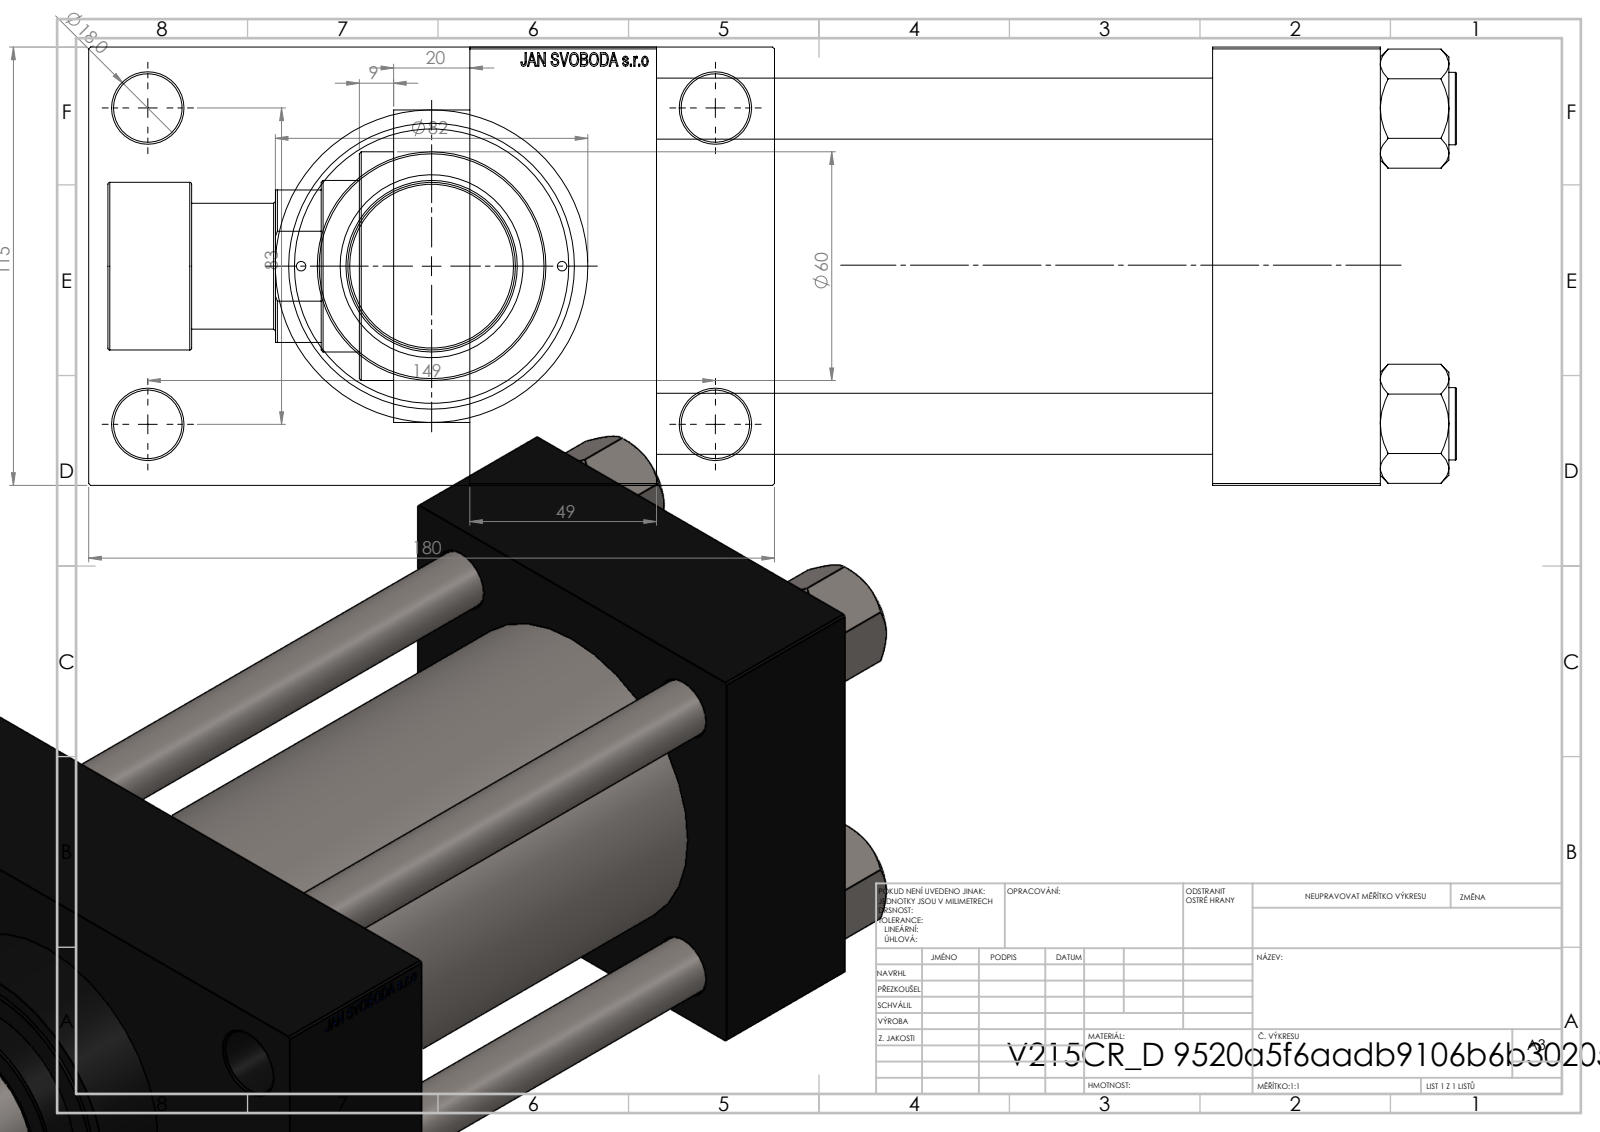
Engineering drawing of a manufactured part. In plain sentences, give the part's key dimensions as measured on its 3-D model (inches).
The part is named "V215CR_ROD_END_F; NUT_M5_D; V215CR_VCP_D; V215CR_D_Body (+2 more)". Its 3-D file was written by "SolidWorks 2019 (CONFIG_CONTROL_DESIGN)". It is 12 solids with 1172 faces: 550 planar, 96 cylindrical and 526 other. Overall it measures 13.937 by 7.087 by 4.528 inches. Its volume is 141 cubic inches and its surface area 588.7 square inches. Round holes: 4 of diameter 0.63, 4 of diameter 0.709, 2 of diameter 0.098, 2 of diameter 0.276, 2 of diameter 1.041, 2 of diameter 1.378, 1 of diameter 1.24, 1 of diameter 1.772, 1 of diameter 1.89, 1 of diameter 2.402, 1 of diameter 2.835, 1 of diameter 3.15. Round bosses or shafts: 4 of diameter 0.748, 1 of diameter 3.386, 1 of diameter 3.228, 1 of diameter 2.362, 1 of diameter 1.732, 1 of diameter 1.299. The main face-to-face distances are 4.528, 1.732, 5.748, 7.677, 1.929, 7.48, 9.409, 1.28, 5.807, 3.937. The hole center spacings are 1.305, 1.652, 2.276, 2.302, 3.256, 3.357, 3.393, 3.513.
